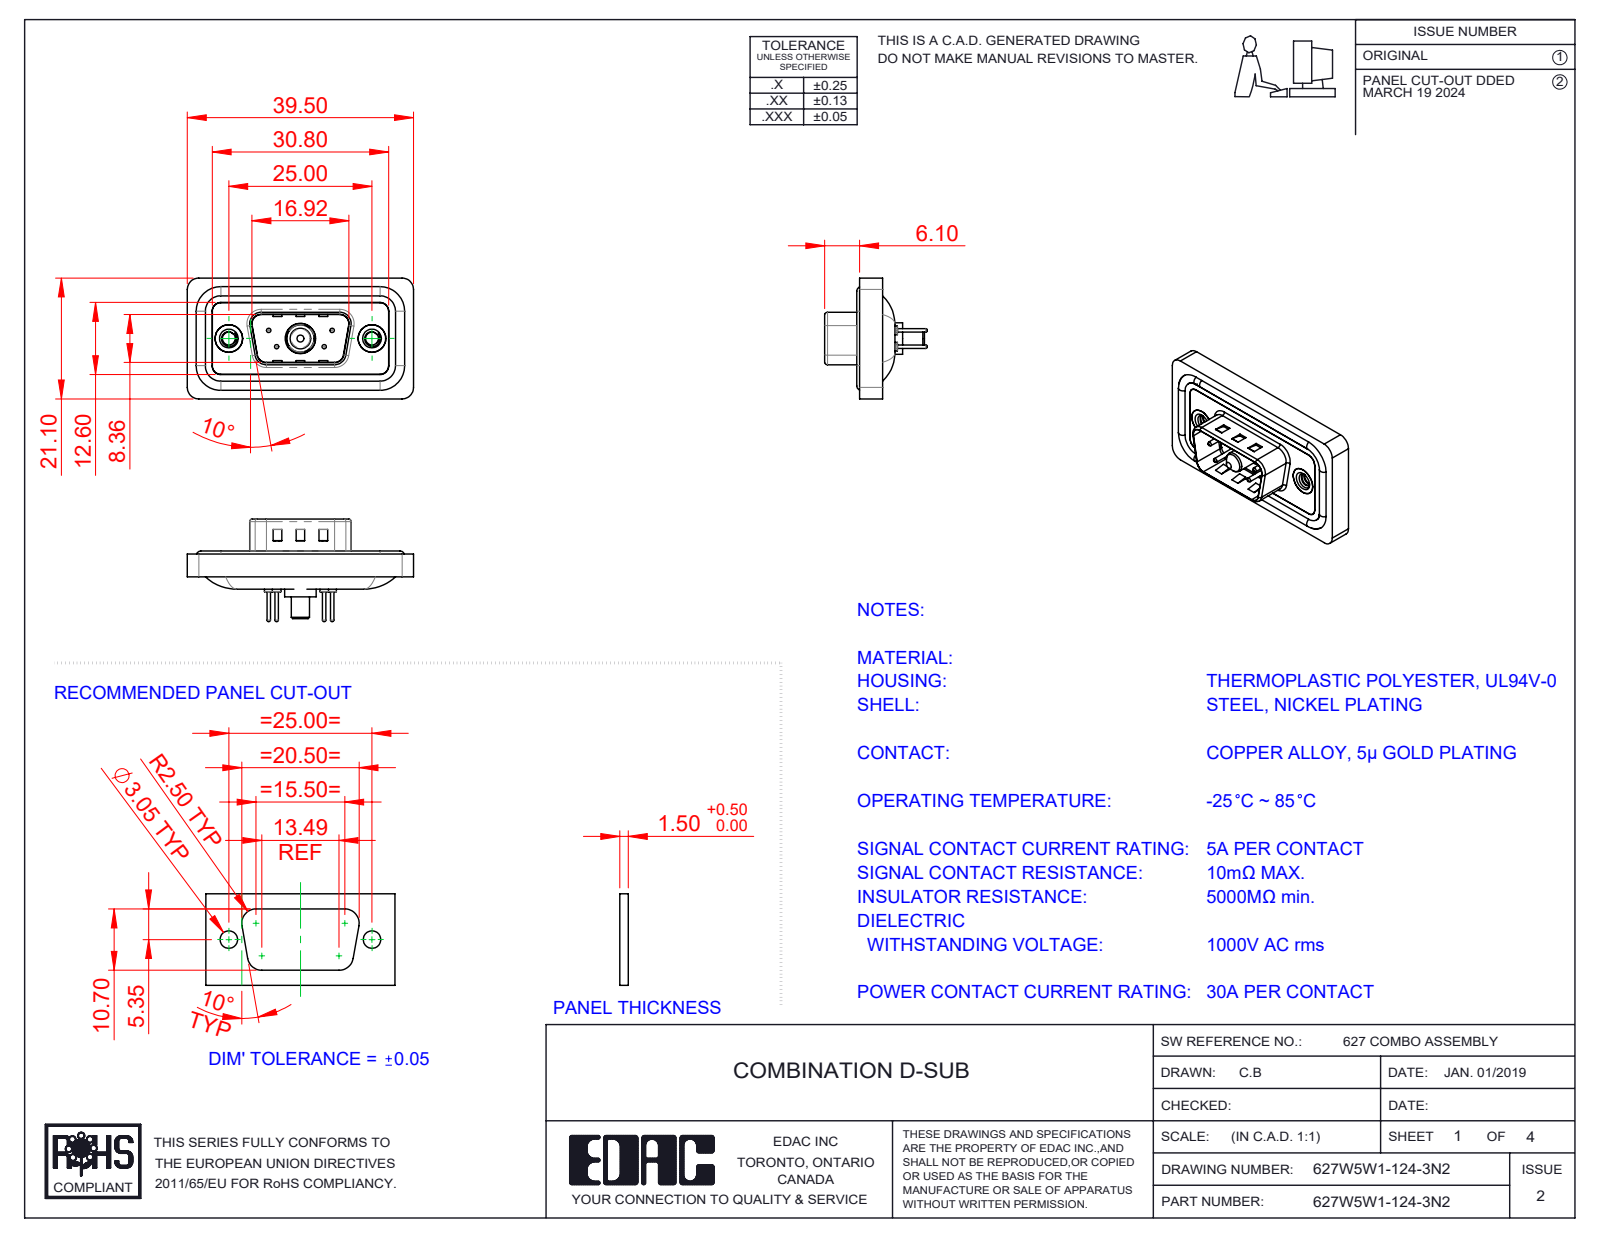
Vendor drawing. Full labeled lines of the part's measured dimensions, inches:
Part name (STEP PRODUCT): Power Pin_30A S; 627W5W1-124-3N2; 627Combo Threaded Rivet_2; 627Combo Shell Rear_09 Contacts (+5 more)
STEP written by: SolidWorks 2023 (CONFIG_CONTROL_DESIGN)
Units: inches
Bodies: 13 solids, 598 faces (183 planar, 255 cylindrical, 160 other)
Overall size (bounding box): 1.555 × 0.831 × 0.705
Volume: 0.268 in³ · Surface area: 10.77 in²
Round holes (diameter × count): ⌀0.03 ×4, ⌀0.063 ×4, ⌀0.079 ×4, ⌀0.089 ×2, ⌀0.157 ×2, ⌀0.189 ×2, ⌀0.197 ×2, ⌀0.191 ×1, ⌀0.209 ×1
Round bosses / shafts (diameter × count): ⌀0.063 ×4, ⌀0.059 ×4, ⌀0.024 ×4, ⌀0.193 ×2, ⌀0.217 ×1, ⌀0.205 ×1, ⌀0.187 ×1, ⌀0.148 ×1
Partial cylindrical surfaces — rounded edges, fillets, slot ends (radius × count): R0.059 ×22, R0.079 ×18, R0.02 ×8, R0.063 ×8, R0.01 ×4, R0.024 ×4, R0.026 ×4, R0.035 ×4
Main face-to-face distances: 0.016, 0.043, 0.114, 0.063, 0.122, 0.059, 0.02, 0.098, 0.157, 0.031
Hole centre spacings: 0.124, 0.225, 0.28, 0.492, 0.713, 0.173, 0.173, 0.327
